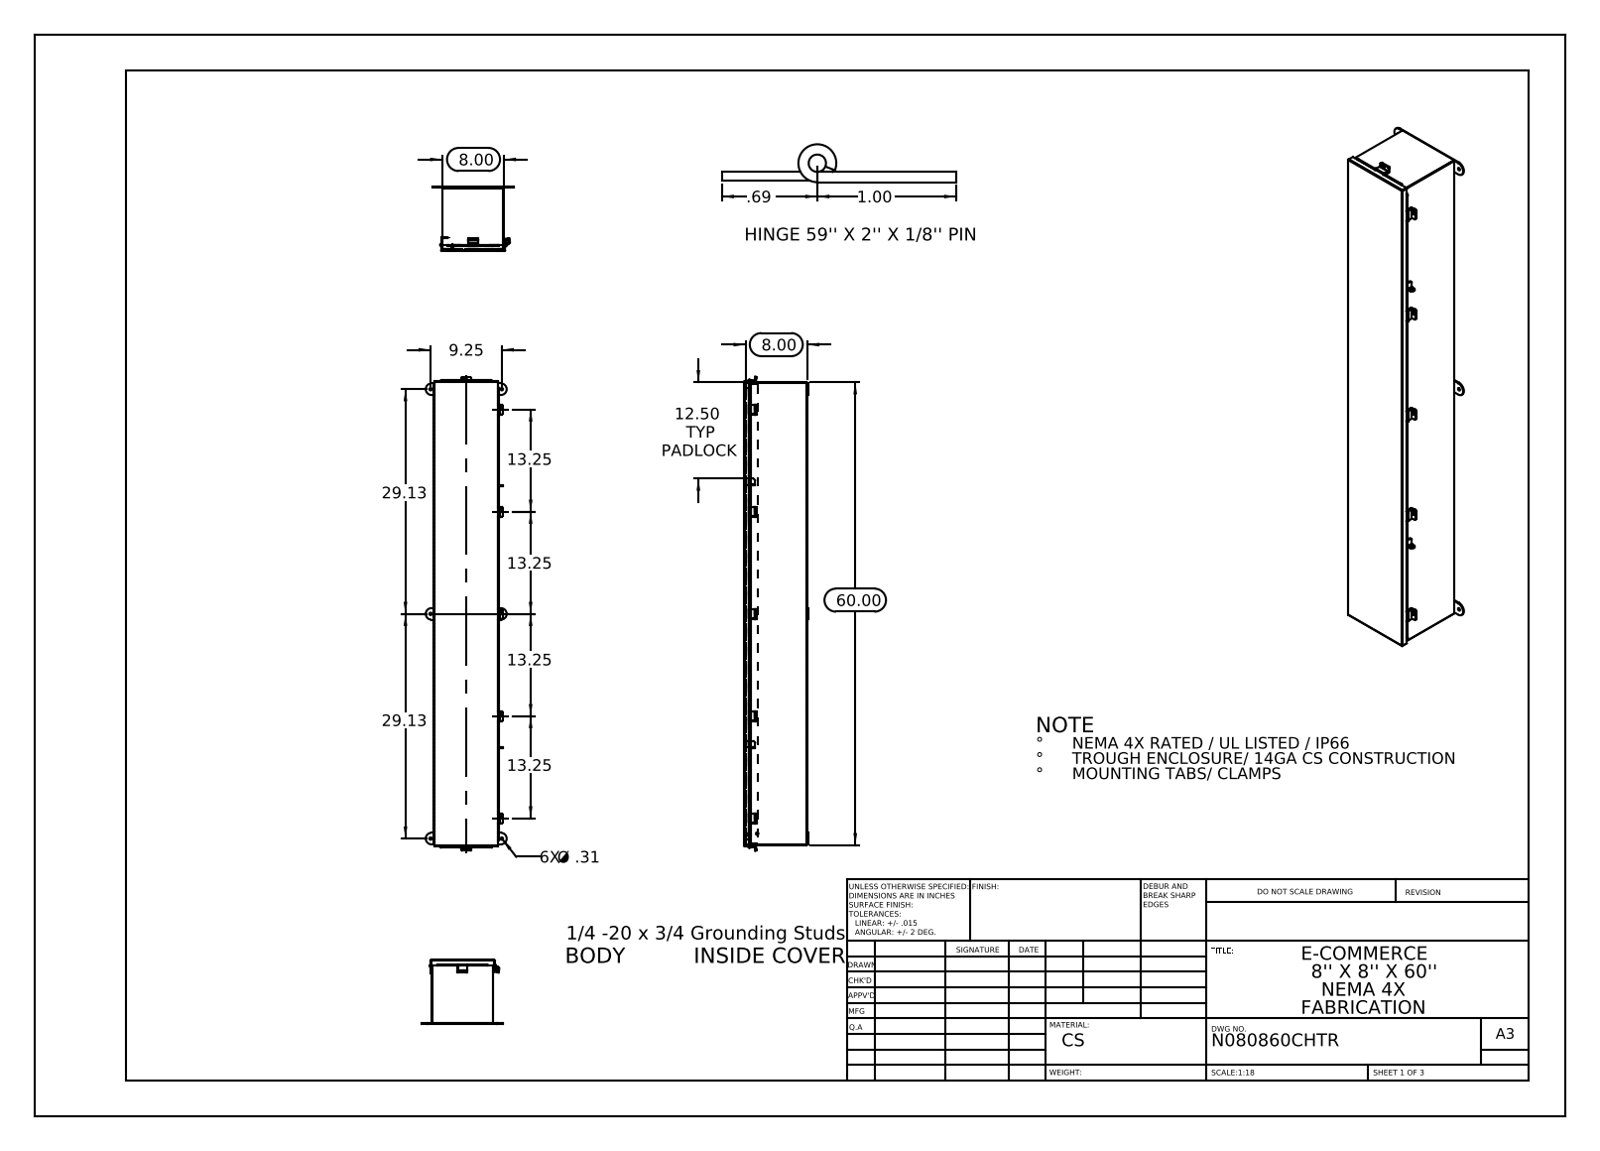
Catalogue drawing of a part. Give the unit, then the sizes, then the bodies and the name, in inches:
Units: inches
Overall size (bounding box): 61.407 × 10.5 × 8.337
Round holes (diameter × count): ⌀0.25 ×7, ⌀0.313 ×6, ⌀0.125 ×1, ⌀0.125 ×1, ⌀0.375 ×1
Round bosses / shafts (diameter × count): ⌀0.315 ×2, ⌀0.236 ×2, ⌀0.273 ×1, ⌀0.25 ×1
Partial cylindrical surfaces — rounded edges, fillets, slot ends (radius × count): R0.125 ×27, R0.133 ×14, R0.009 ×12, R0.013 ×10, R0.088 ×10, R0.083 ×6, R0.1 ×6, R0.75 ×6
Main face-to-face distances: 0.075, 7.925, 8.128, 8, 7.85, 8.203, 8.053, 0.149, 8.074, 0.074
Hole centre spacings: 13.25, 29.125, 30.559, 9.25, 26.5, 39.75, 58.25, 58.98
Volume: 179.3 in³ · Surface area: 4 813 in²
Bodies: 27 solids, 1681 faces (1002 planar, 659 cylindrical, 20 other)
Part name (STEP PRODUCT): N080860SSCHTR JIC Enclosure Template; N080860SSCHTR; N080860SSCHTR JIC Clamp Bracket; N080860SSCHTR JIC Mounting Bracket (+8 more)
STEP written by: SolidWorks 2013 (CONFIG_CONTROL_DESIGN)
